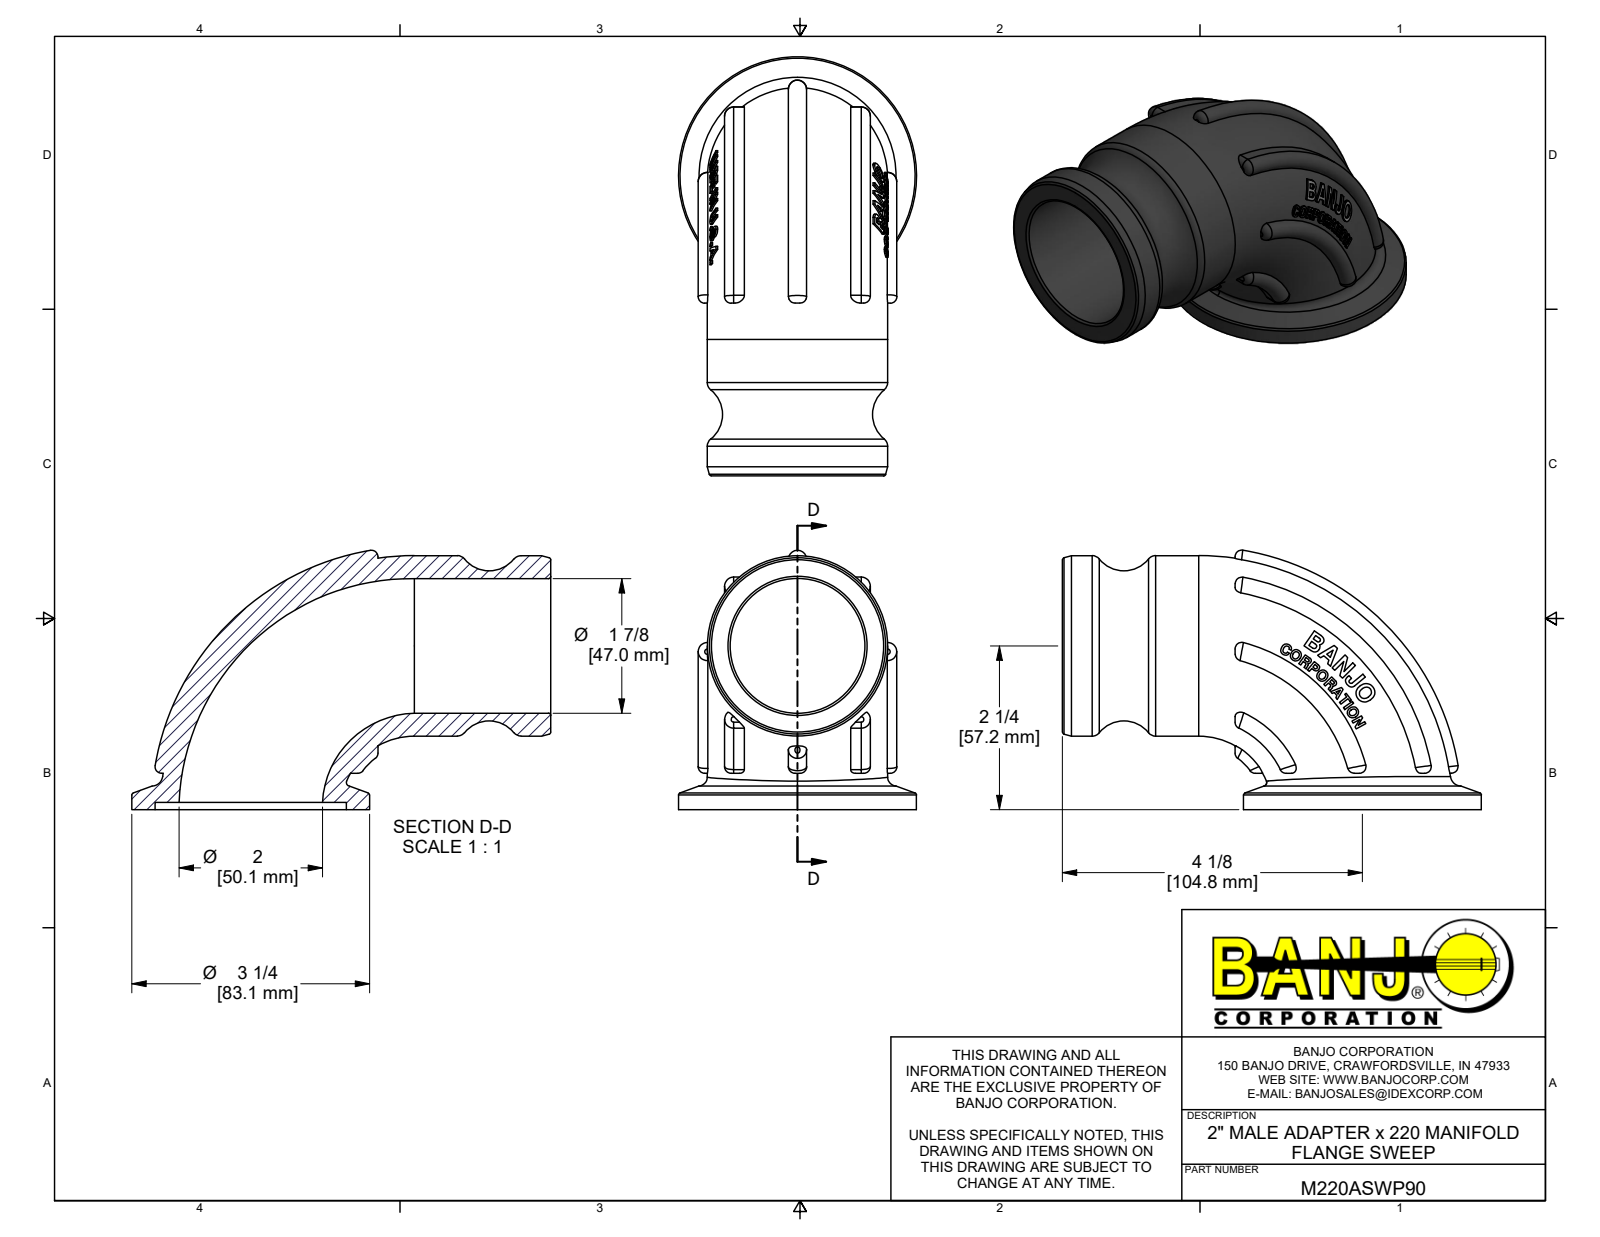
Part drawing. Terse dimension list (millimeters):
name: M220ASWP90
written by: Autodesk Inventor 2012 (AUTOMOTIVE_DESIGN)
unit: mm
bodies: 1 solid, 423 faces (211 planar, 17 cylindrical, 195 other)
size: 146.3 × 90.6 × 83.1
volume: 187 300 mm³; area: 57 030 mm²
holes: 1× ⌀47, 1× ⌀66.8
bosses: 1× ⌀83.1, 1× ⌀63
rounds: 4× R2.3, 1× R31.7, 1× R82.6
face distances: 2.5, 60.3, 12.7, 10.2, 1, 1, 1.3, 5.1, 0.9, 0.8
